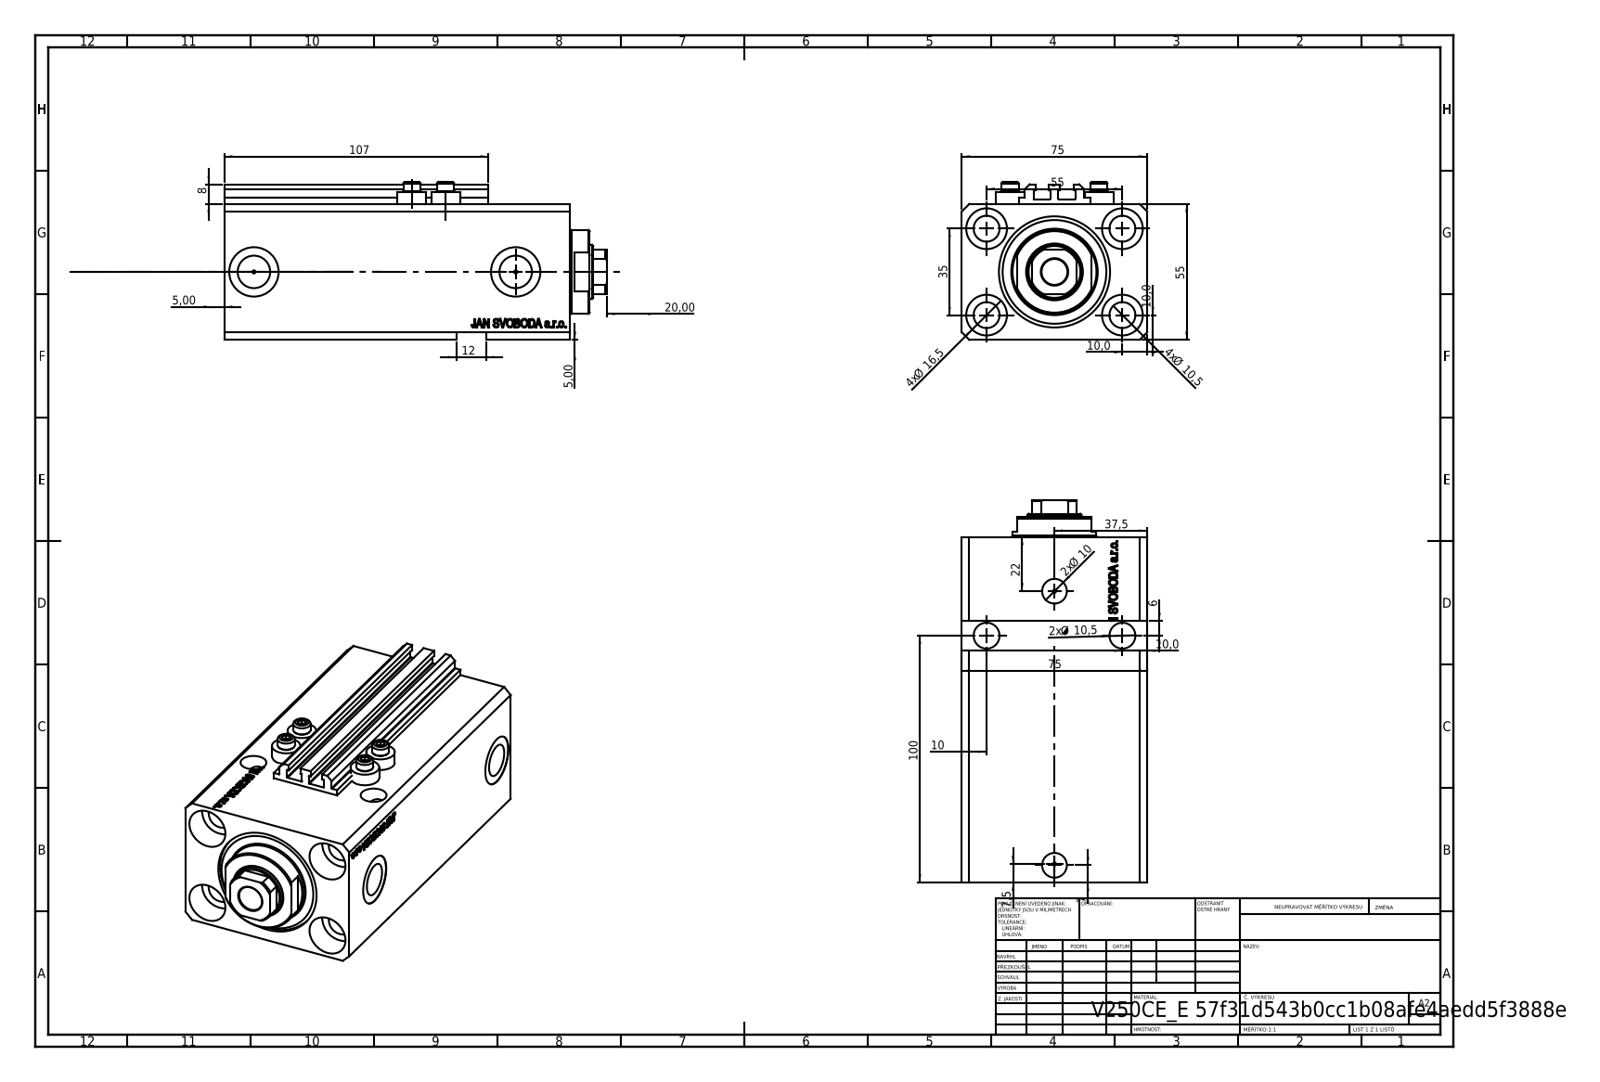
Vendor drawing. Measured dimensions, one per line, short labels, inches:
name: V250CE_E_Body; V250CE_C_VCP; ALLEN BOLT V250CE; V250CE_VC_E
written by: SolidWorks 2019 (CONFIG_CONTROL_DESIGN)
unit: in
bodies: 8 solids, 1080 faces (518 planar, 138 cylindrical, 424 other)
size: 6.098 × 2.953 × 2.52
volume: 29.78 in³; area: 182.1 in²
holes: 7× ⌀0.413, 4× ⌀0.049, 4× ⌀0.157, 4× ⌀0.65, 2× ⌀0.394, 2× ⌀0.518, 2× ⌀0.787, 1× ⌀0.866, 1× ⌀1.26, 1× ⌀1.772
bosses: 4× ⌀0.457, 4× ⌀0.276, 1× ⌀1.339
rounds: 10× R0.008, 1× R0.413
face distances: 2.165, 2.953, 0.39, 5.512, 4.445, 1.067, 0.118, 2.244, 4.055, 5.122
hole spacings: 1.283, 2.165, 0.535, 0.555, 1.016, 1.294, 1.324, 1.378
